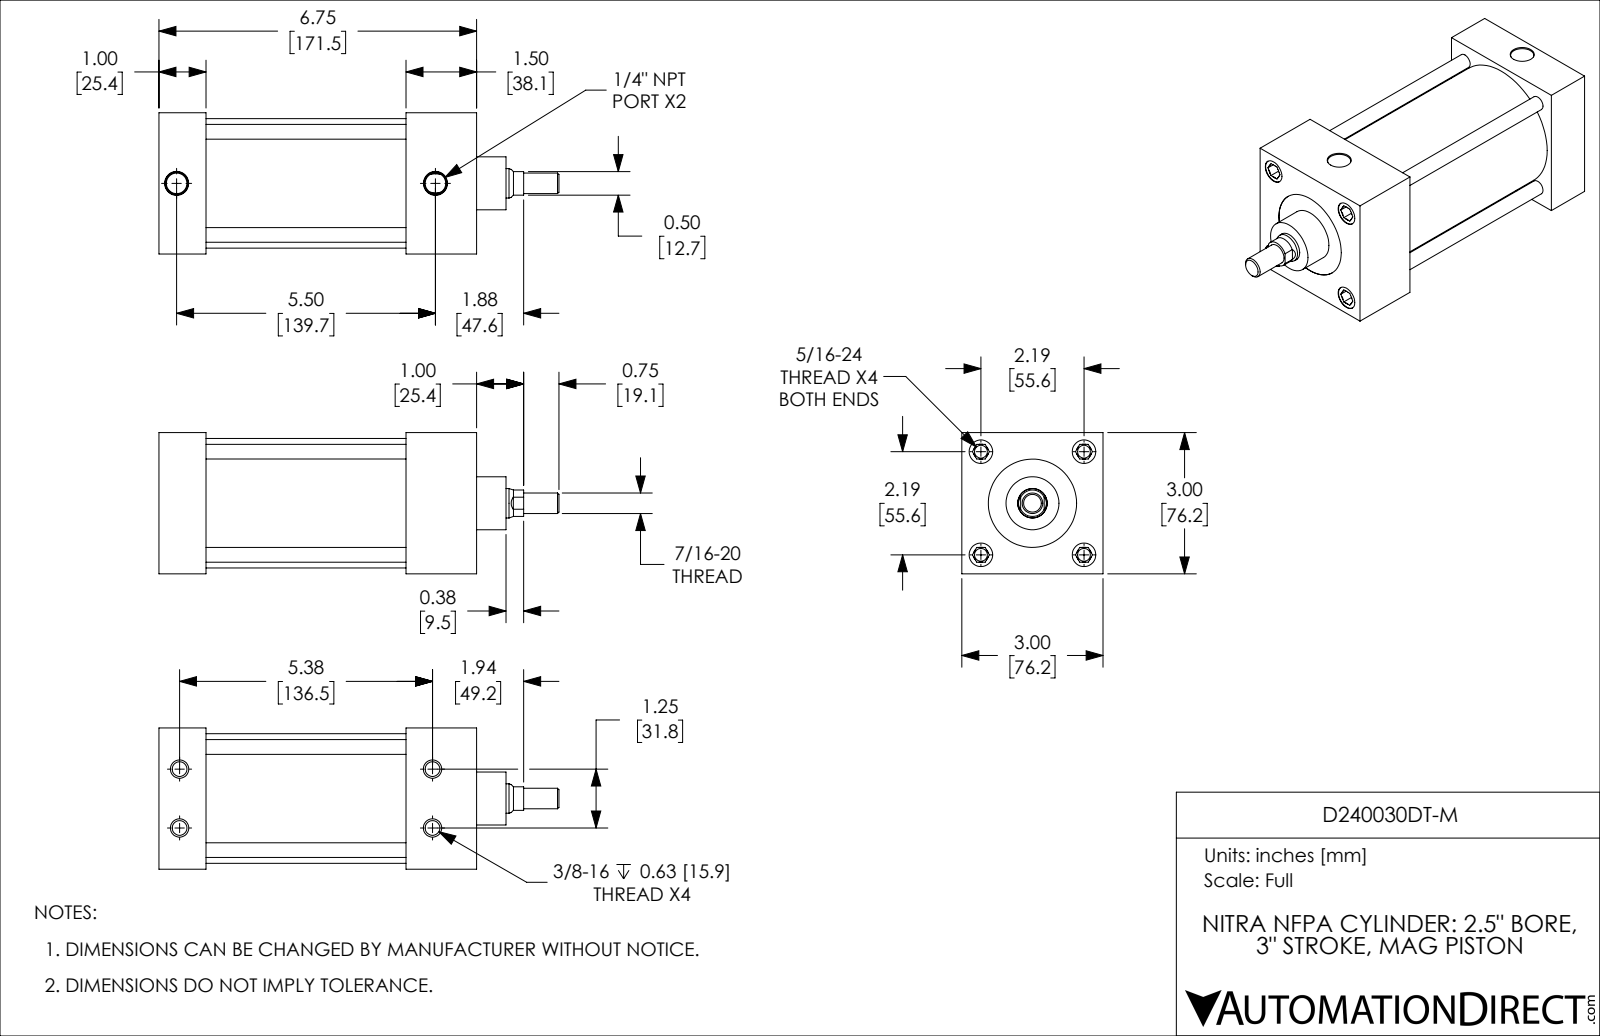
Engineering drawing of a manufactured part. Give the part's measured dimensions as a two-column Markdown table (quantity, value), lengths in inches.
| quantity | value |
| --- | --- |
| part name | D240030DT-M_PISTON_KK1; D240030DT-M; D240030DT-M_BODY |
| STEP written by | SolidWorks 2019 (CONFIG_CONTROL_DESIGN) |
| units | inches |
| bodies | 2 solids, 200 faces (58 planar, 62 cylindrical, 80 other) |
| overall size | 8.5 × 3 × 3 |
| volume | 34.96 in³ |
| surface area | 199.3 in² |
| round holes (diameter × count) | 0.272 × 4, 0.313 × 4, 0.5 × 4, 0.438 × 2, 0.626 × 1, 1.875 × 1, 2.501 × 1 |
| round bosses / shafts (diameter × count) | 0.312 × 4, 2.751 × 1, 2.499 × 1, 1.125 × 1, 0.624 × 1, 0.437 × 1 |
| partial cylindrical surfaces (radius × count) | 0.281 × 1 |
| main face-to-face distances | 3, 1, 5.25, 4.25, 6.75, 5.75, 1.5, 1.25, 2.25, 4.5 |
| hole center spacings | 1.548, 2.19, 5.473, 0.628, 0.628, 1.25, 3.097, 5.375 |
